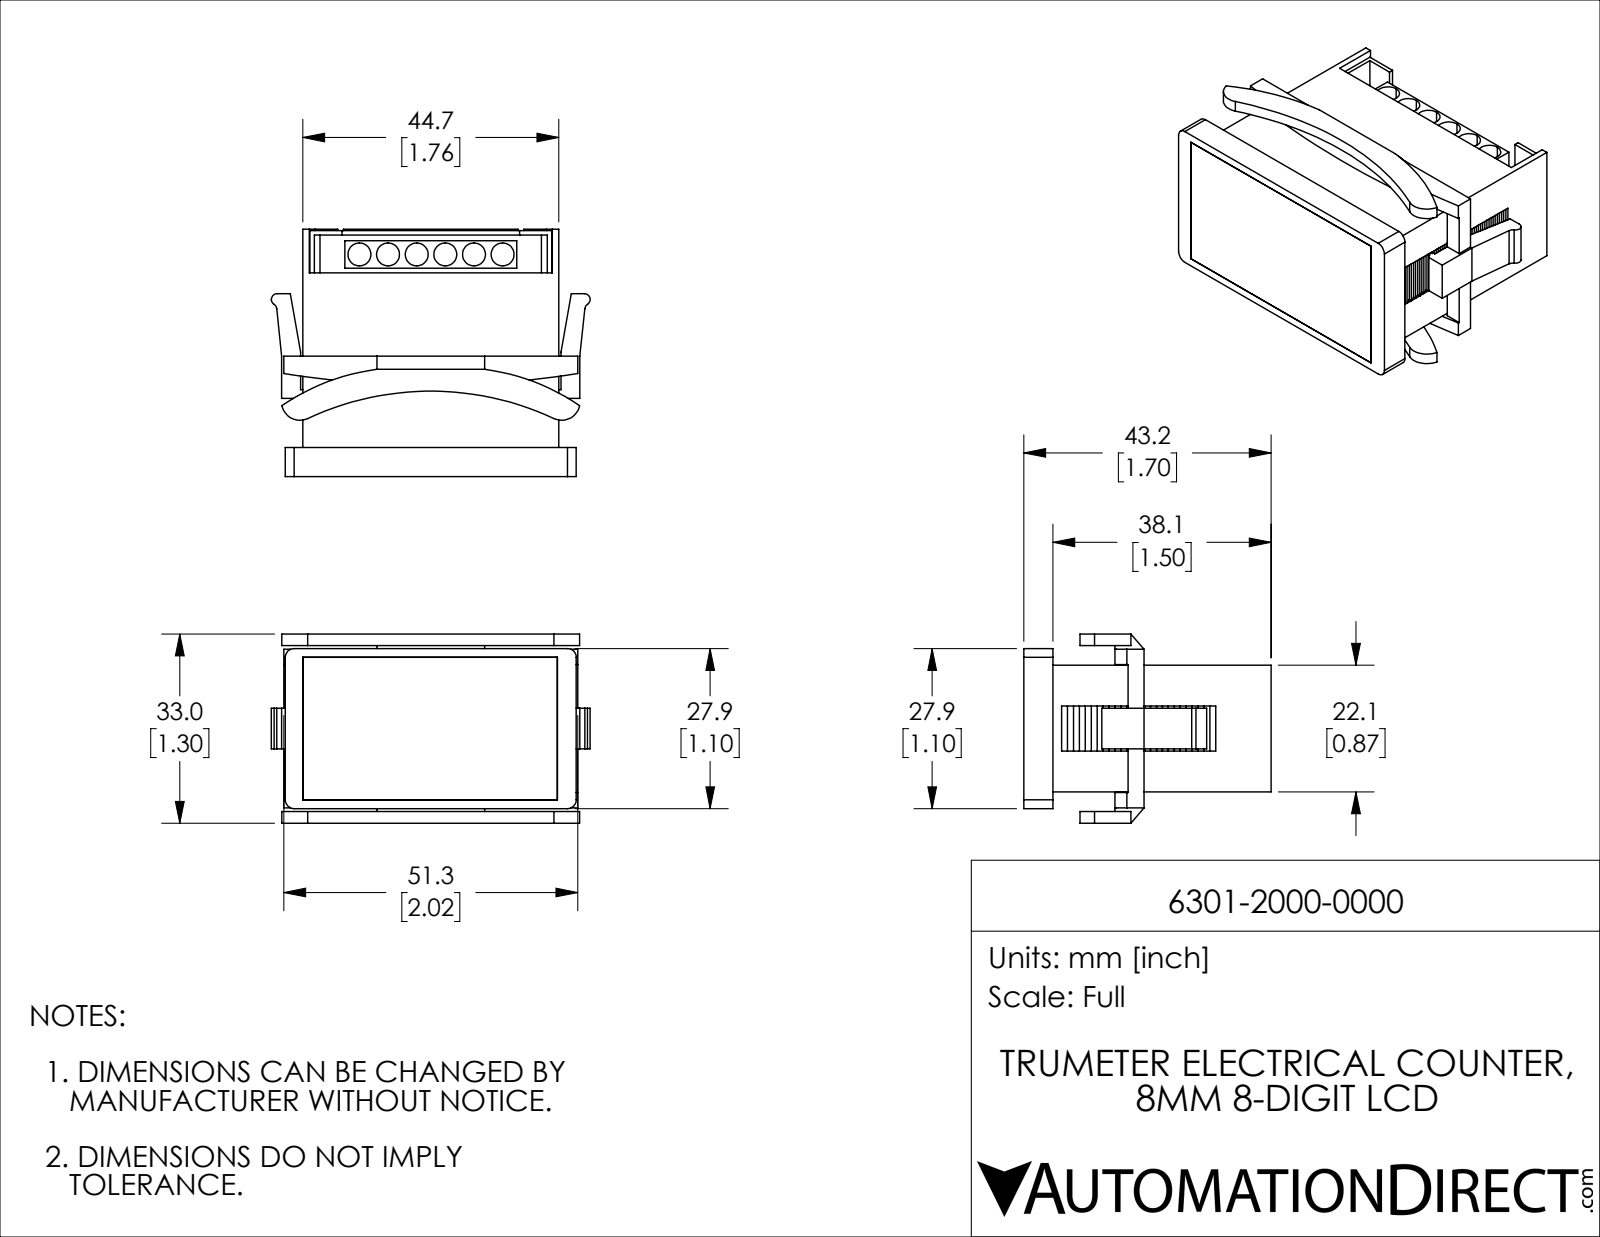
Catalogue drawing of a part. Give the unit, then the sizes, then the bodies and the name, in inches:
Units: inches
Overall size (bounding box): 2.191 × 1.7 × 1.3
Round holes (diameter × count): ⌀0.157 ×6
Partial cylindrical surfaces — rounded edges, fillets, slot ends (radius × count): R0.04 ×4, R0.06 ×4, R0.126 ×2, R1.5 ×2, R2 ×1, R6.28 ×1
Main face-to-face distances: 0.045, 0.079, 0.825, 0.034, 0.03, 0.049, 0.04, 0.06, 0.87, 0.791
Hole centre spacings: 0.197, 0.394, 0.591, 0.787, 0.984
Volume: 1.393 in³ · Surface area: 48.67 in²
Bodies: 6 solids, 464 faces (431 planar, 33 cylindrical, 0 other)
Part name (STEP PRODUCT): 6301-2000-0000
STEP written by: SolidWorks 2021 (CONFIG_CONTROL_DESIGN)
